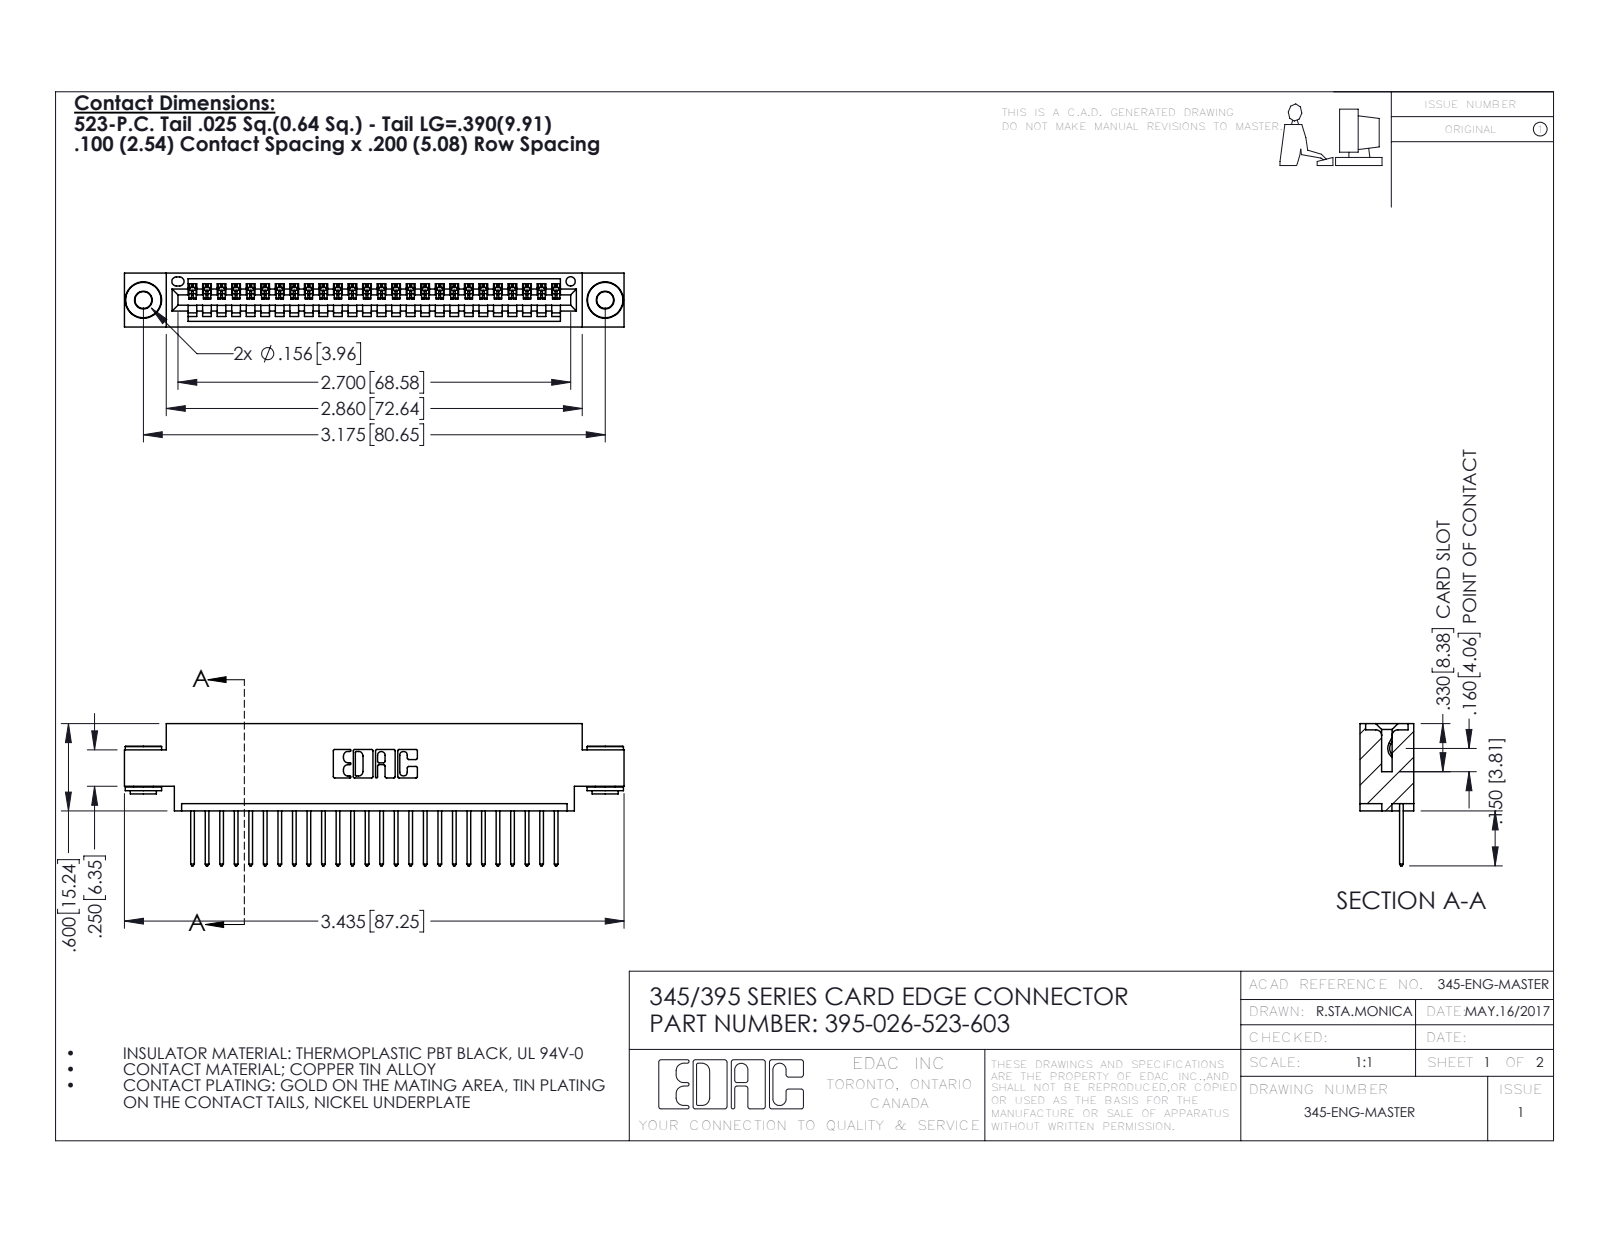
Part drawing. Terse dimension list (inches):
name: 395-026-523-603; 345-250-002_345-250-002-102; 345-292-001_345-293-123; 345 Part_0.170 Offset - 0.156 Dia-TH
written by: SolidWorks 2016 (CONFIG_CONTROL_DESIGN)
unit: in
bodies: 29 solids, 1676 faces (1134 planar, 534 cylindrical, 8 other)
size: 3.435 × 0.977 × 0.37
volume: 0.491 in³; area: 16.82 in²
holes: 2× ⌀0.116, 2× ⌀0.156, 1× ⌀0.064
bosses: 2× ⌀0.25, 2× ⌀0.18, 2× ⌀0.136
rounds: 52× R0.006, 52× R0.01, 22× R0.01, 6× R0.007, 6× R0.031, 3× R0.026, 2× R0.031, 2× R0.04
face distances: 0.072, 0.298, 0.37, 0.2, 0.098, 0.272, 0.025, 0.225, 0.175, 0.149
hole spacings: 0.27, 2.94, 3.175
